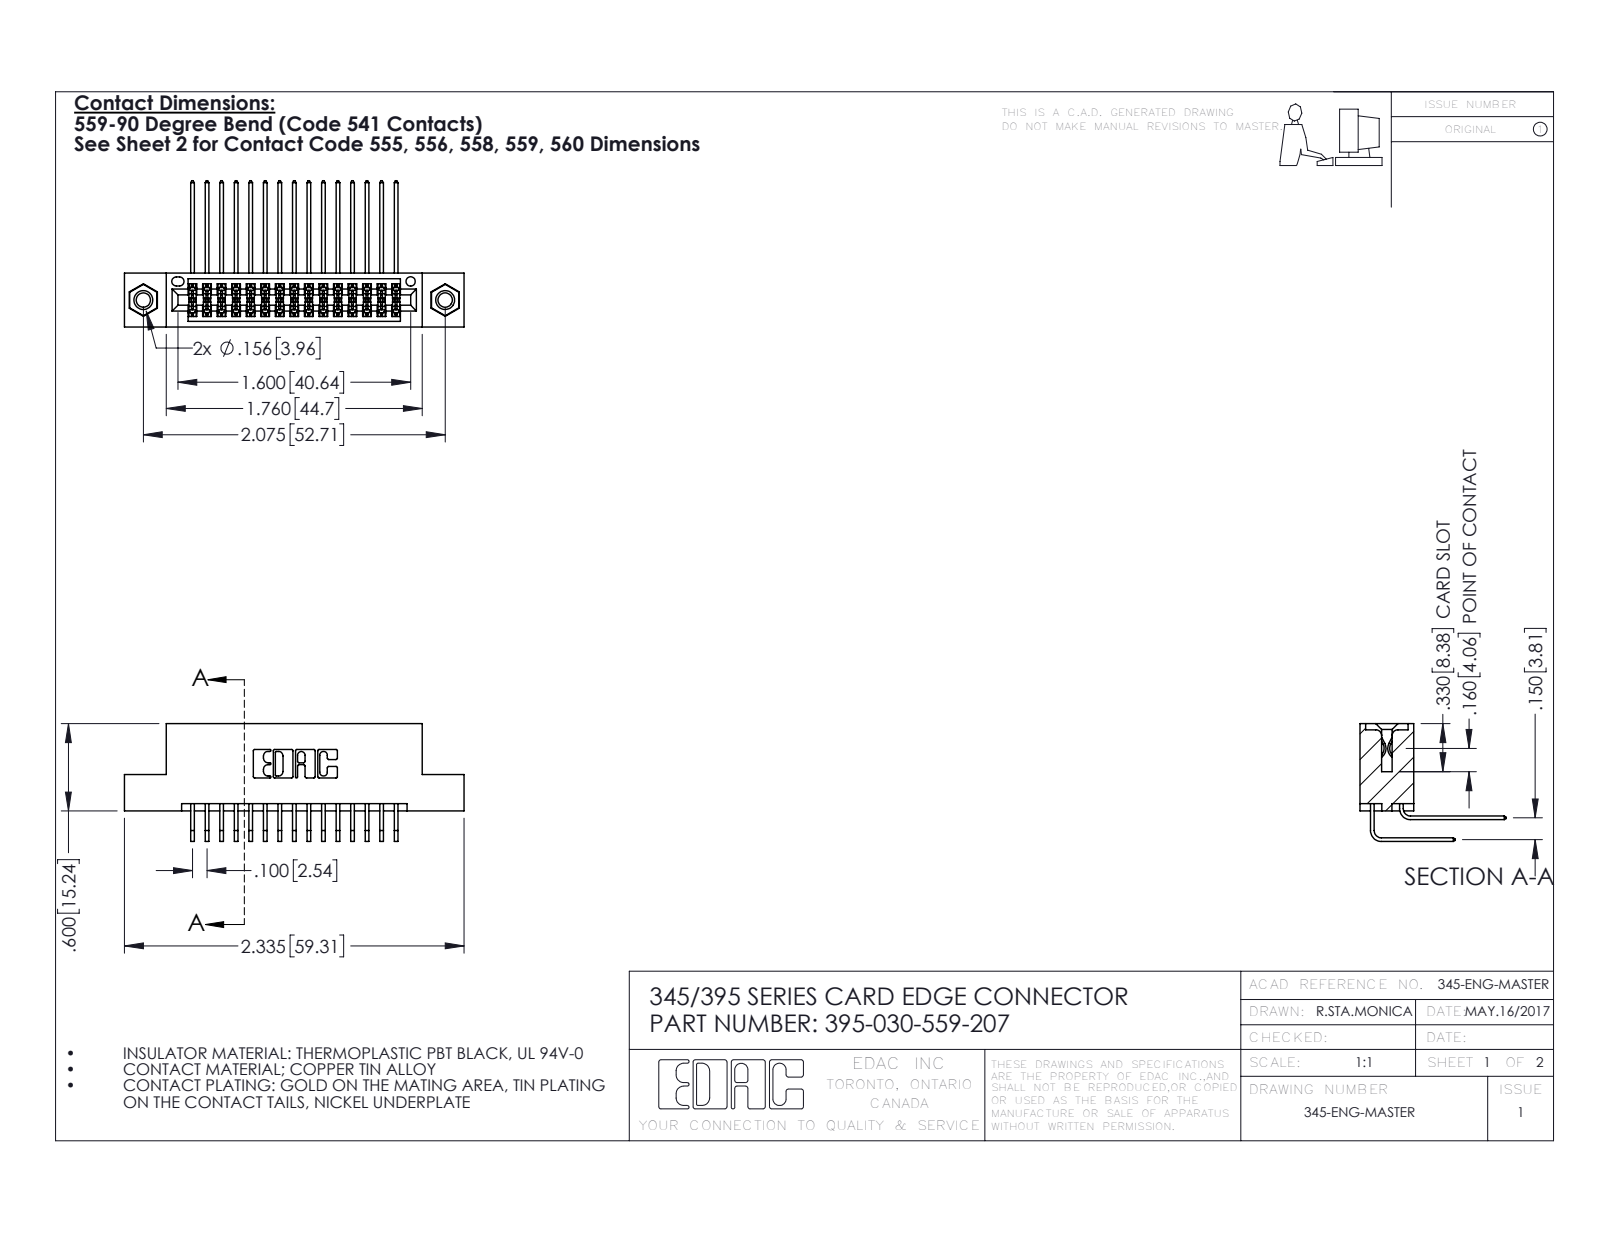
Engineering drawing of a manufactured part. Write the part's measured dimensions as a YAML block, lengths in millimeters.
part_name: "345 Part_Flush Mounting Lugs - 0.156 Dia-TI; 345-292-001_559 Tail - 2; 345-292-001_558 559 Tail - 1; 345-250-001_345-250-005-103 (+1 more)"
step_written_by: "SolidWorks 2016 (CONFIG_CONTROL_DESIGN)"
units: millimeters
bodies: {solids: 33, faces: 1746, planar: 1162, cylindrical: 568, other: 16}
overall_size: [59.3, 25.5, 20.5]
volume: 5670
surface_area: 8703
round_holes:
  - {diameter: 2.5, count: 2}
  - {diameter: 3.2, count: 2}
  - {diameter: 4, count: 2}
  - {diameter: 1.6, count: 1}
round_bosses_or_shafts:
  - {diameter: 3.9, count: 2}
partial_cylinders:
  - {radius: 0.2, count: 45}
  - {radius: 0.3, count: 22}
  - {radius: 0.2, count: 6}
  - {radius: 0.8, count: 6}
  - {radius: 0.7, count: 3}
  - {radius: 0.4, count: 2}
  - {radius: 0.5, count: 2}
  - {radius: 0.6, count: 2}
face_to_face_distances: [1.8, 7.6, 5.1, 9.4, 2.5, 6.9, 0.6, 5.7, 3.8, 4.4]
hole_center_spacings: [6.9, 46.8, 52.7]
